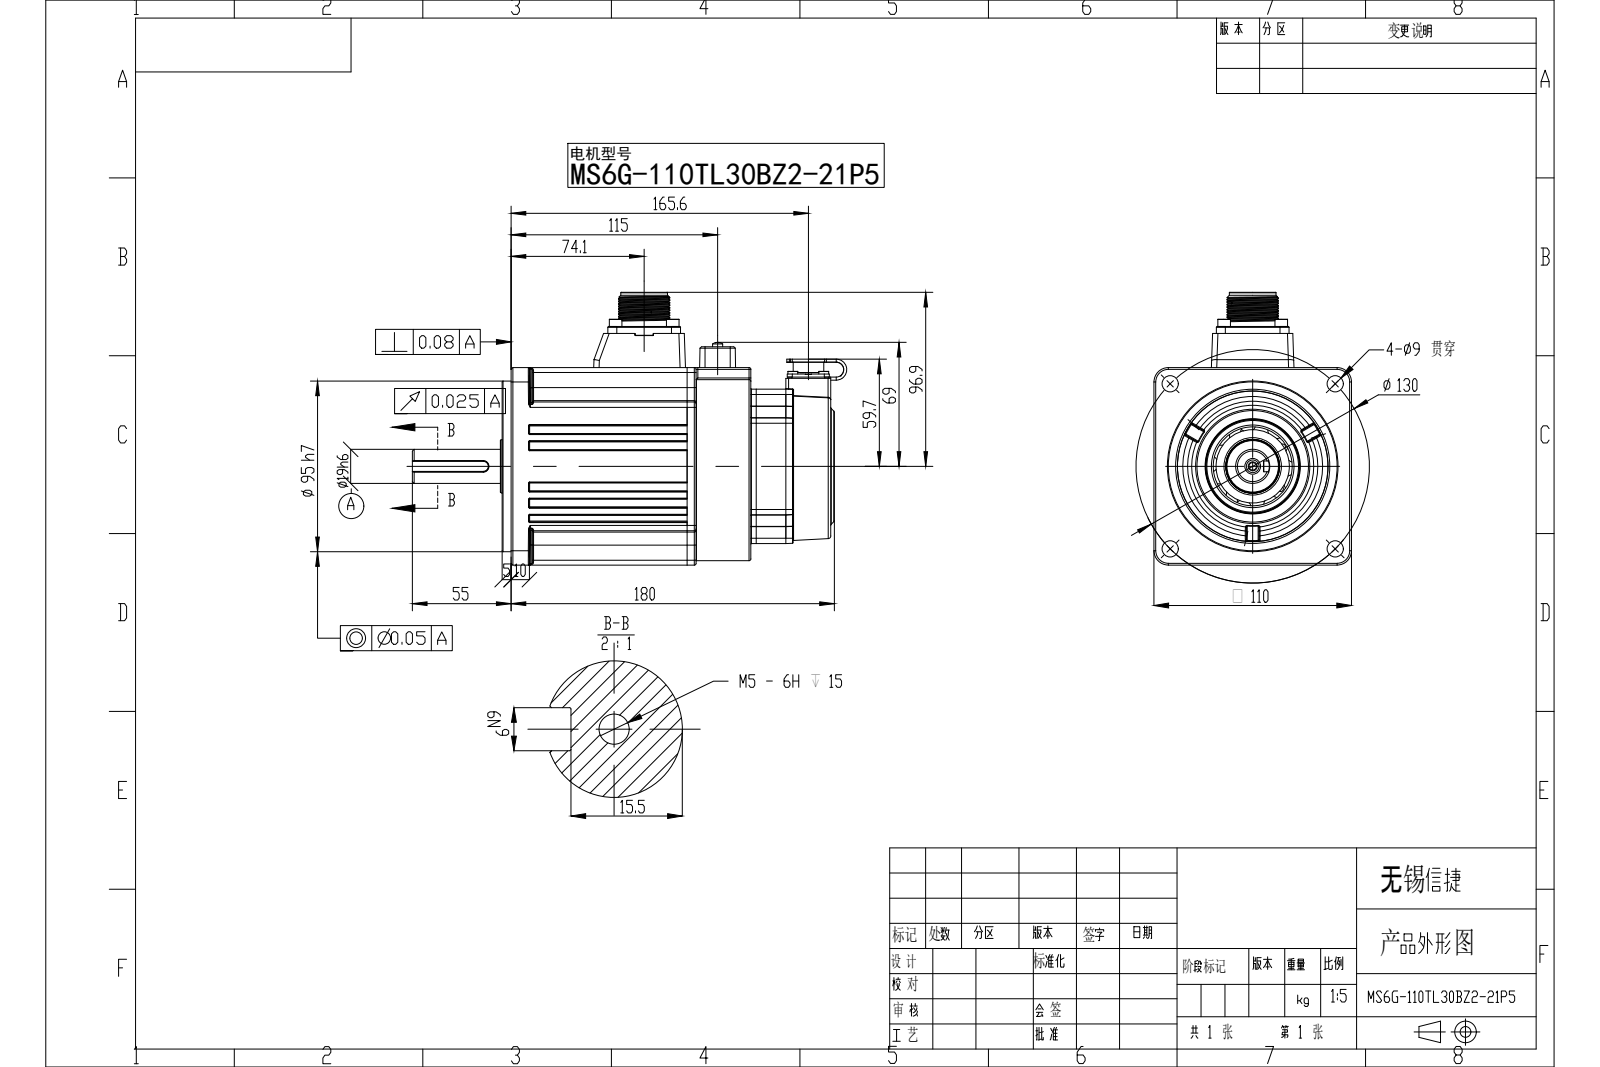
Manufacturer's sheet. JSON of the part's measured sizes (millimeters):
{"part_name": "MS6G-110TL30BZ2-21P5", "step_written_by": "SolidWorks 2022 (CONFIG_CONTROL_DESIGN)", "units": "millimeters", "bodies": {"solids": 0, "faces": 1082, "planar": 309, "cylindrical": 417, "other": 356}, "overall_size": [241.9, 156, 116.83], "round_holes": [[4.5, 4], [5.8, 4], [4.2, 1], [5, 1], [43.94, 1], [45.68, 1], [95, 1]], "round_bosses_or_shafts": [[7, 4], [5.5, 4], [2.4, 4], [5.6, 2], [105, 1], [52, 1], [46, 1], [40.8, 1]], "partial_cylinders_radius": [[0.3, 97], [0.5, 49], [1, 30], [3, 23], [0.2, 22], [8, 8], [1.5, 4], [2.3, 4]], "face_to_face_distances": [109.99, 109.98, 5, 103, 180, 158, 82, 98, 2, 185], "hole_center_spacings": [27.52, 45.28, 53.93, 57.46, 64.03, 81.26, 88.28, 99.72]}
